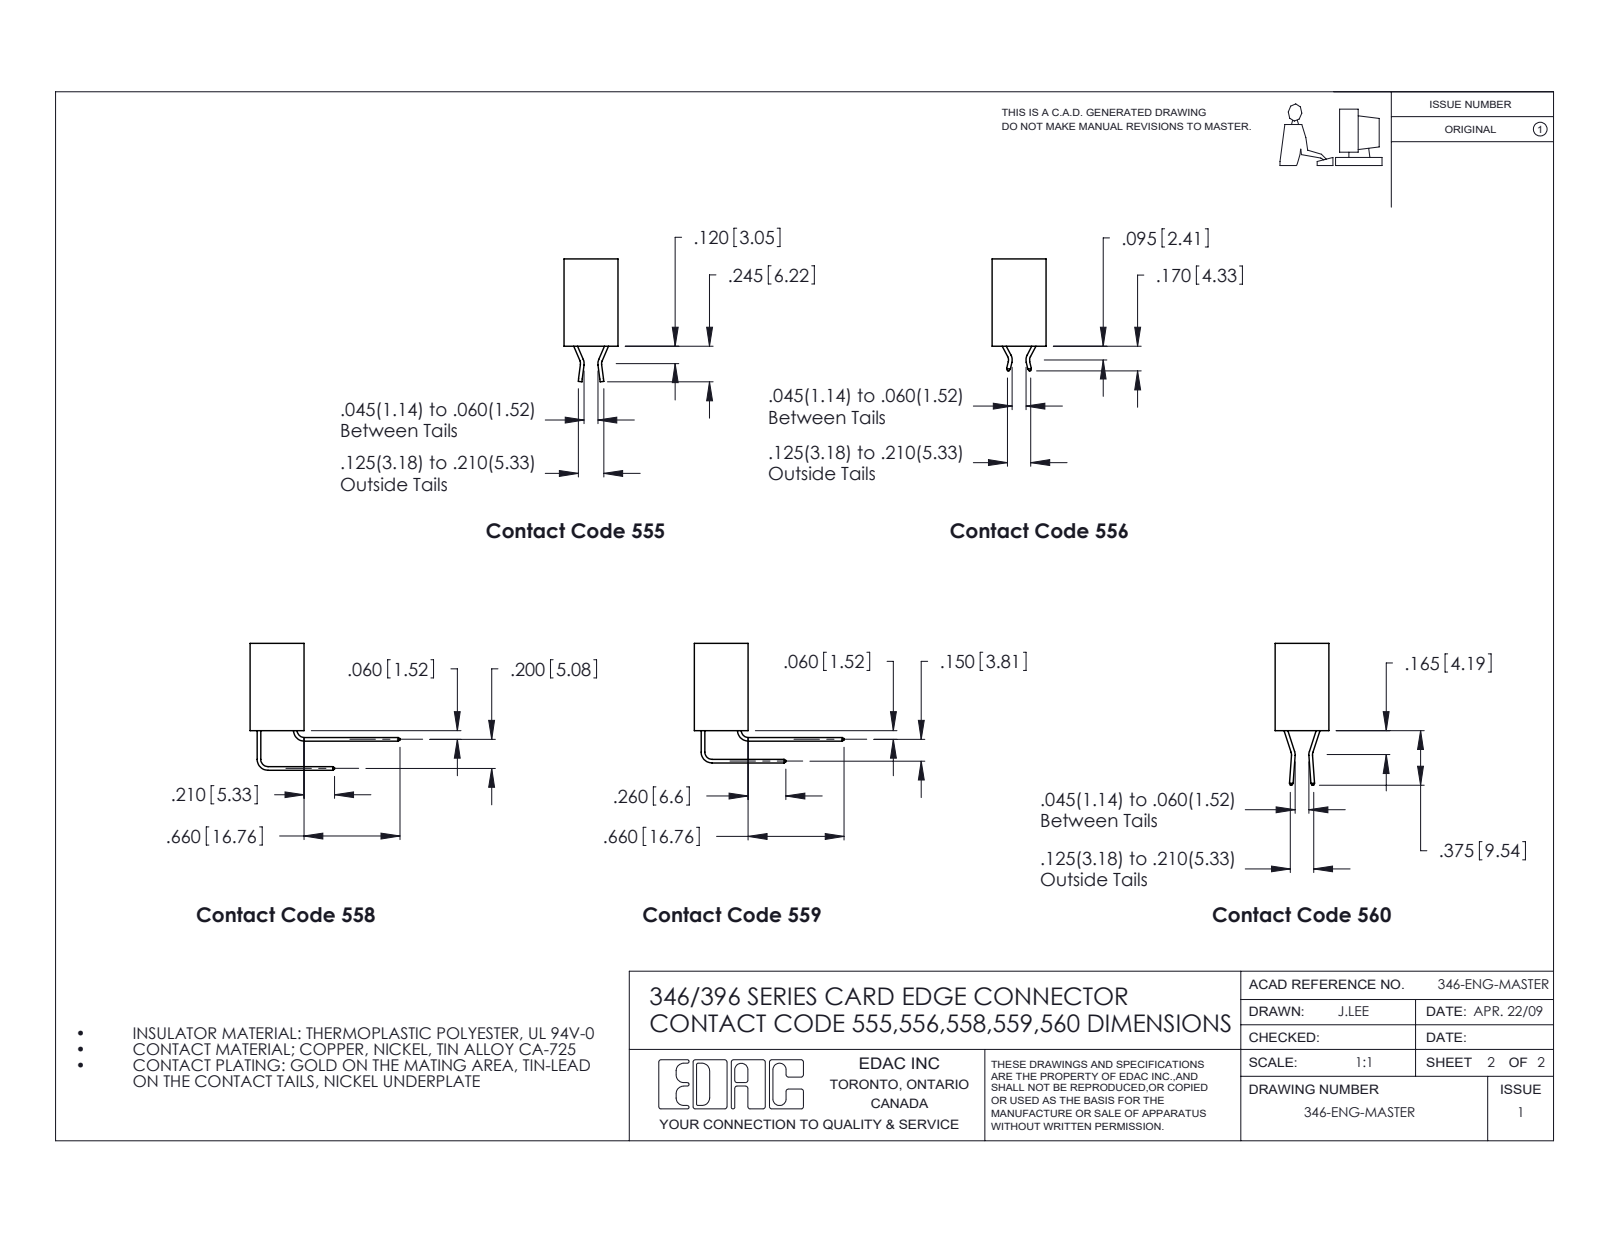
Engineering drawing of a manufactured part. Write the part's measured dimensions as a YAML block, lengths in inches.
part_name: "346-100-541-201; 346 Part_No Mounting Lugs; 345-292-001_345-293-141"
step_written_by: "SolidWorks 2020 (CONFIG_CONTROL_DESIGN)"
units: inches
bodies: {solids: 101, faces: 5314, planar: 3572, cylindrical: 1742, other: 0}
overall_size: [6.535, 1.35, 0.37]
volume: 1.062
surface_area: 41.77
round_holes:
  - {diameter: 0.064, count: 1}
partial_cylinders:
  - {radius: 0.006, count: 150}
  - {radius: 0.01, count: 100}
  - {radius: 0.01, count: 22}
  - {radius: 0.007, count: 6}
  - {radius: 0.031, count: 6}
  - {radius: 0.026, count: 3}
  - {radius: 0.014, count: 2}
  - {radius: 0.022, count: 2}
face_to_face_distances: [0.048, 0.322, 0.25, 0.072, 0.298, 0.025, 0.37, 0.275, 0.225, 0.148]
